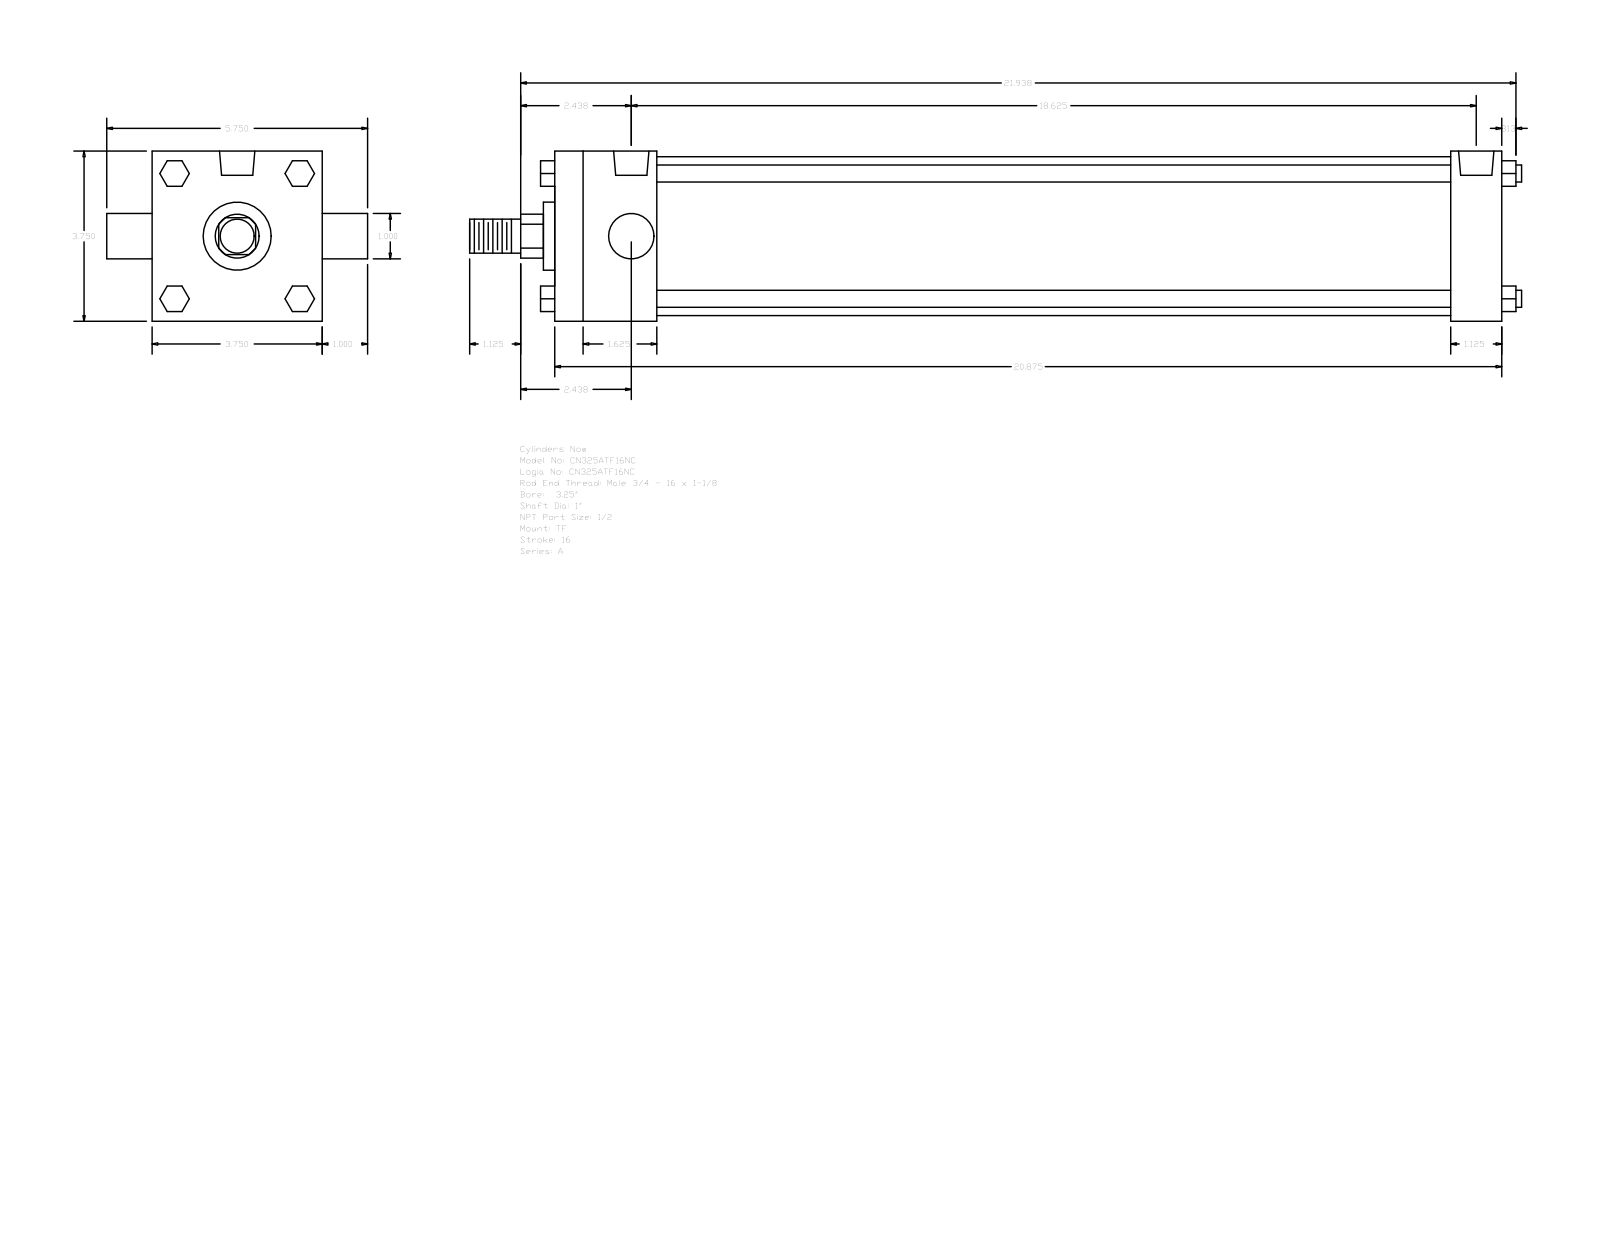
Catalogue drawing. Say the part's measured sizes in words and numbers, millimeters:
The part is named "A_TF__0325_1". Its 3-D file was written by "GSSL Pune (CONFIG_CONTROL_DESIGN)". It is 0 solids with 120 faces: 92 planar, 28 cylindrical and 0 other. Overall it measures 588.96 by 146.05 by 95.25 millimeters. Round holes: 3 of diameter 8.73, 2 of diameter 19.77. Round bosses or shafts: 4 of diameter 9.53, 2 of diameter 25.4, 1 of diameter 88.9, 1 of diameter 38.1, 1 of diameter 19.05. Partial cylindrical surfaces (rounded edges, fillets, slot ends): 1 of radius 12.29. The main face-to-face distances are 95.24, 530.22, 28.57, 57.15, 501.65, 444.5, 473.07, 14.28, 35.05, 60.71. The hole center spacings are 3.18, 469.9, 466.72, 473.08.
